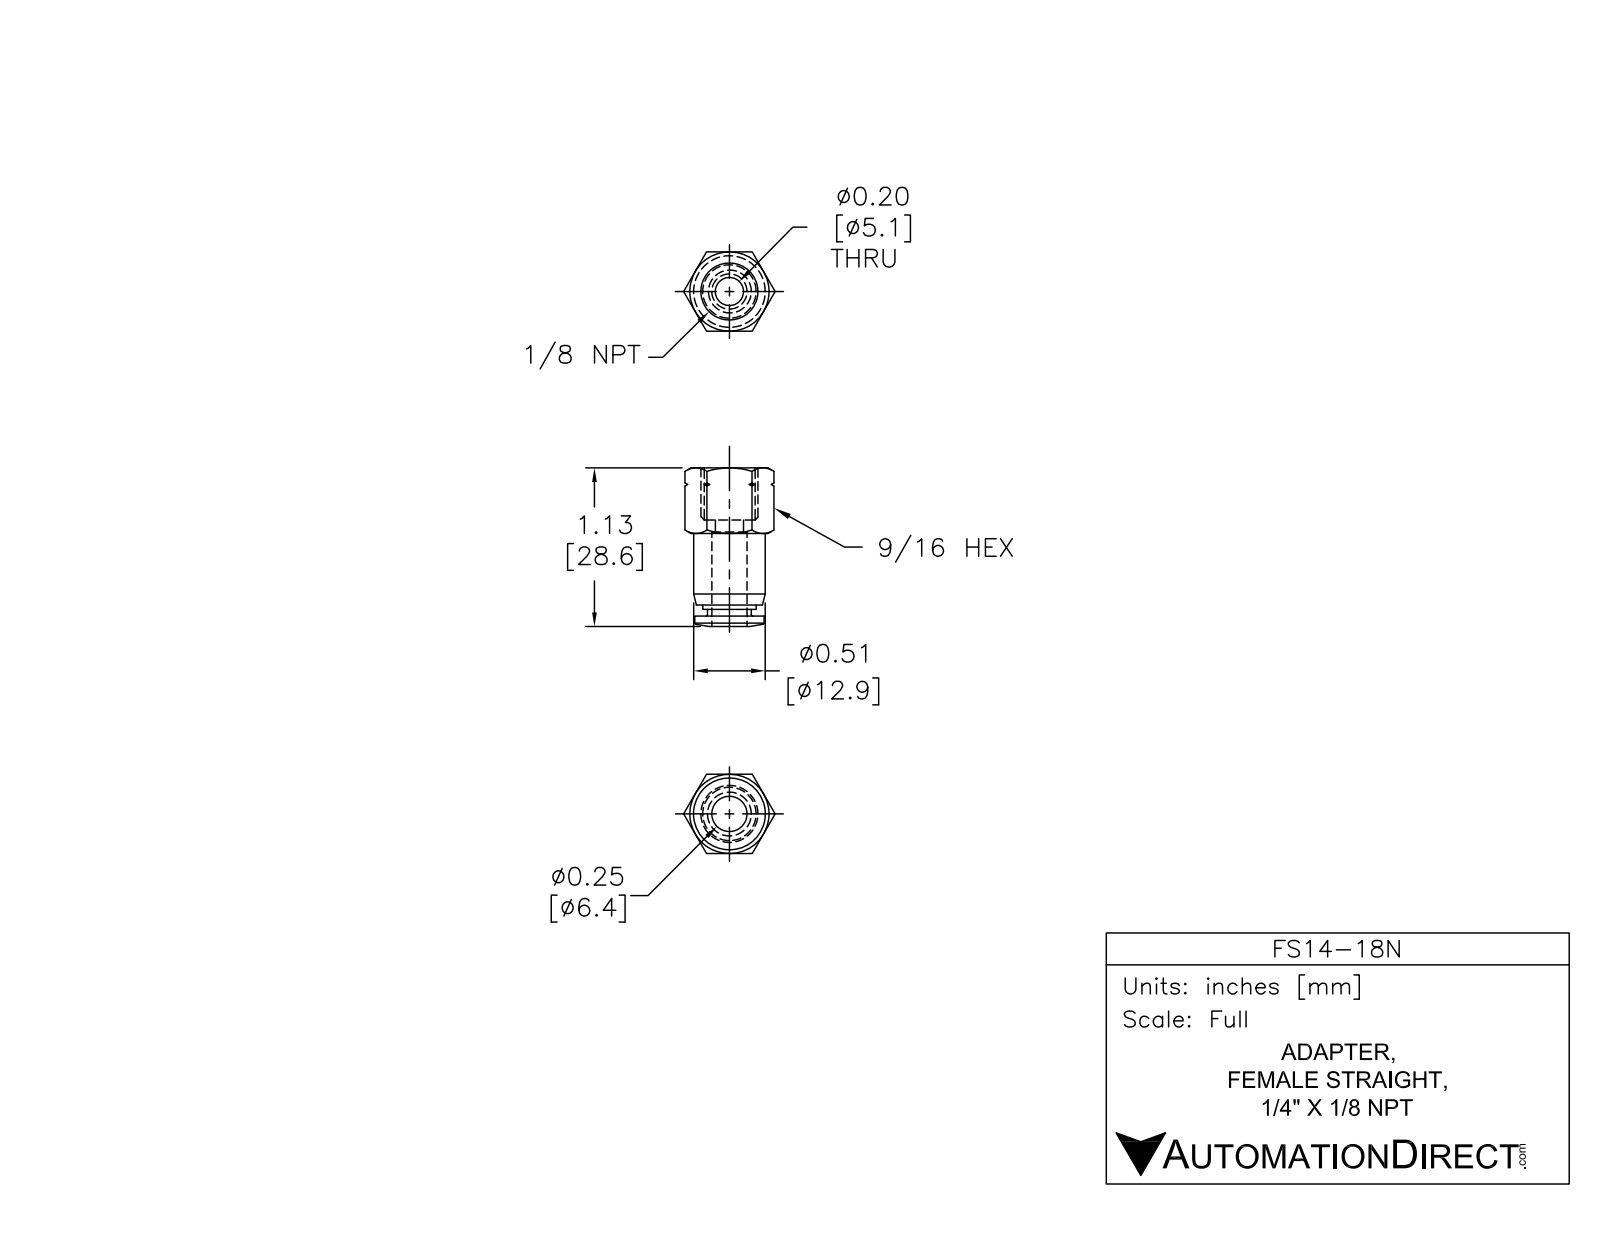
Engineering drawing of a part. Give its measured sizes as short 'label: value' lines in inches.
name: FS14-18N
written by: SolidWorks 2015 (AUTOMOTIVE_DESIGN)
unit: in
bodies: 1 solid, 63 faces (13 planar, 12 cylindrical, 38 other)
size: 1.134 × 0.636 × 0.551
volume: 0.164 in³; area: 3.568 in²
holes: 1× ⌀0.197, 1× ⌀0.258
bosses: 1× ⌀0.512, 1× ⌀0.496, 1× ⌀0.382, 1× ⌀0.313
face distances: 0.551, 1.059, 0.374, 0.685, 0.98, 0.606, 0.079, 0.469, 0.094, 0.512
